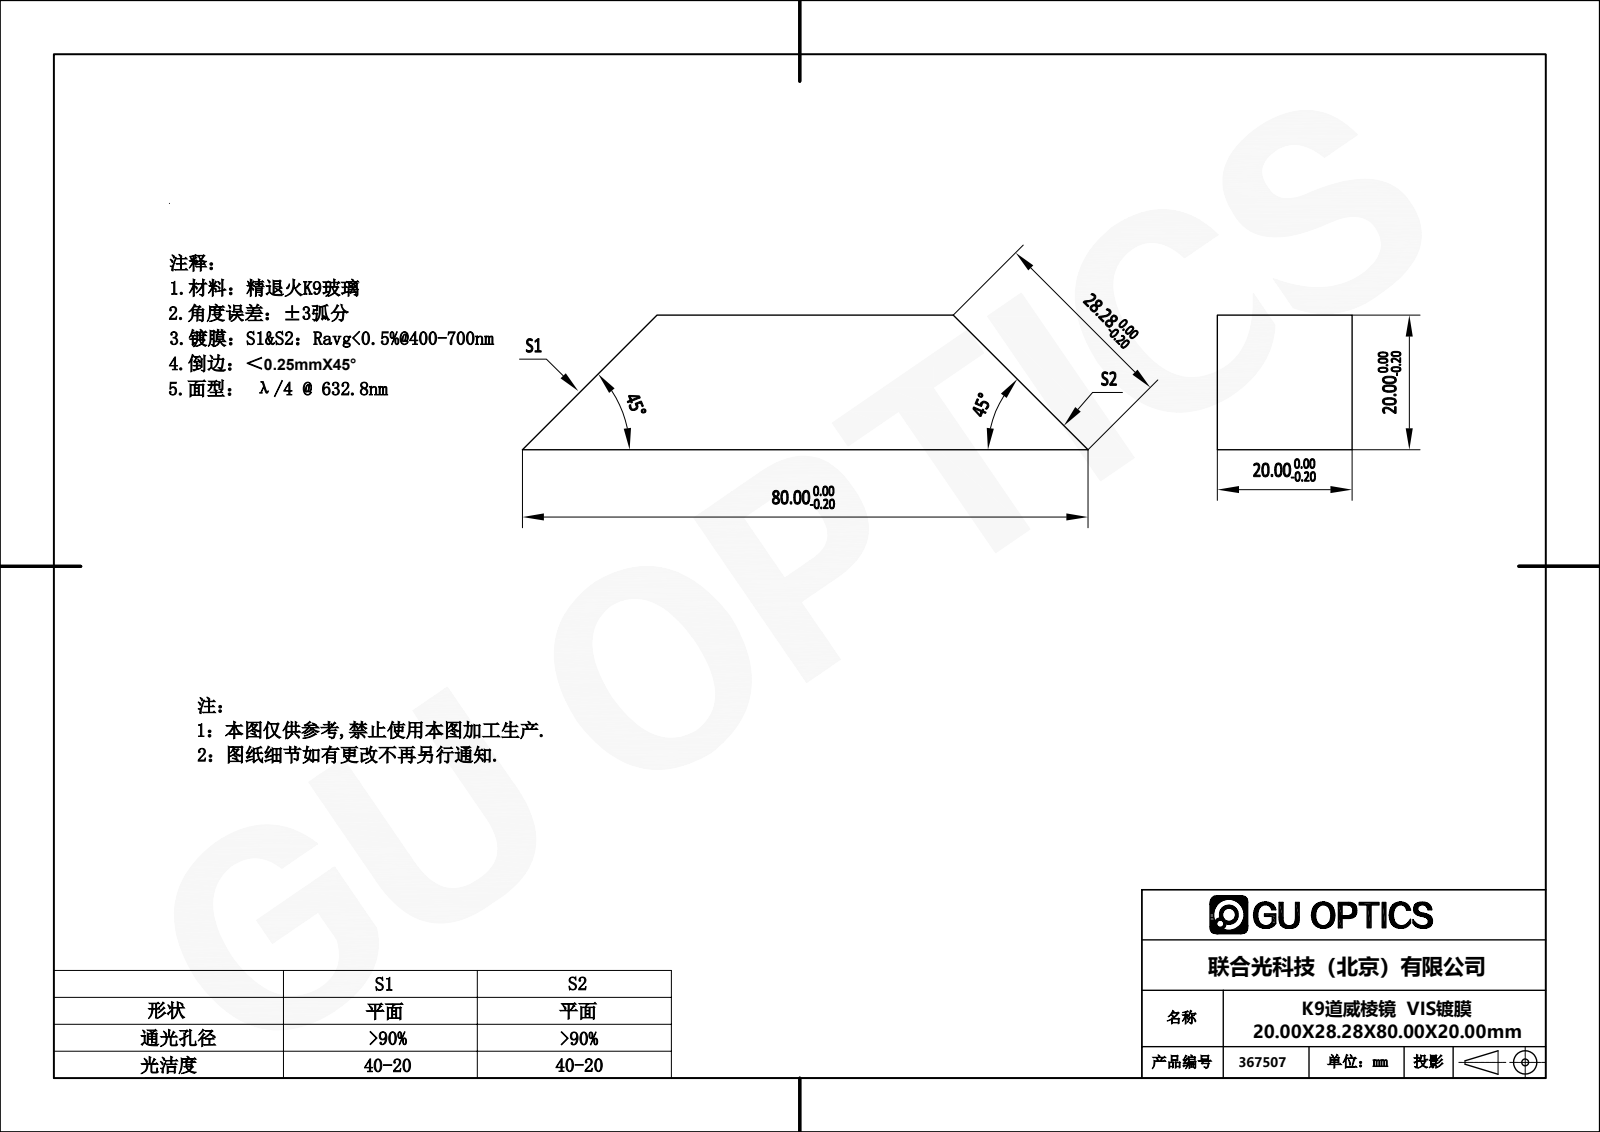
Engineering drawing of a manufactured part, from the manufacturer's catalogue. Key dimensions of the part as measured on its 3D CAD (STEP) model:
Part name (STEP PRODUCT): 367507
STEP written by: SolidWorks 2020 (CONFIG_CONTROL_DESIGN)
Units: millimetres
Bodies: 1 solid, 6 faces (6 planar, 0 cylindrical, 0 other)
Overall size (bounding box): 80 × 20 × 20
Volume: 24 000 mm³ · Surface area: 5 931 mm²
Main face-to-face distances: 20
